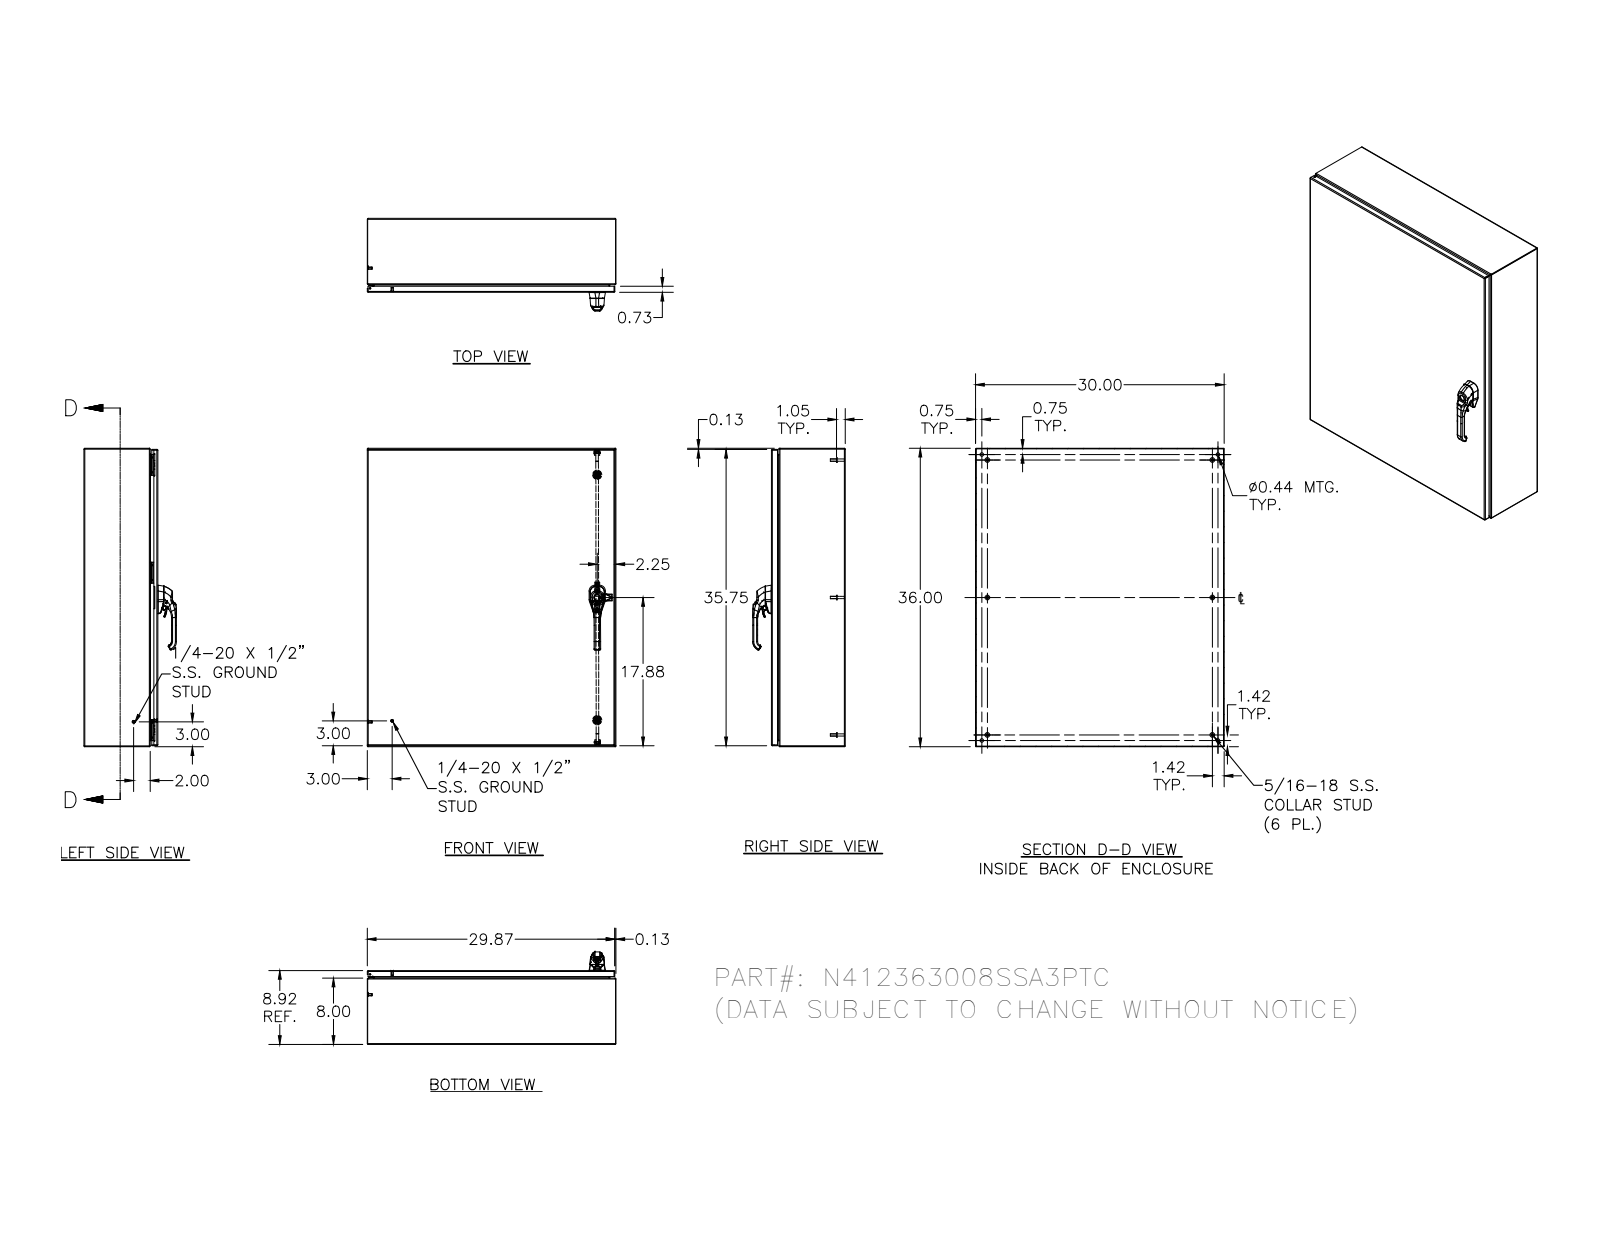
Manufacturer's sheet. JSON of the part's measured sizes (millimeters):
{"part_name": "N412363008SSA3PTC; N412363008SSA3PTCBKP; N4123630SSA3PTCLID; HFW328176 (+8 more)", "step_written_by": "Autodesk Inventor 2011 (AUTOMOTIVE_DESIGN)", "units": "millimeters", "bodies": {"solids": 74, "faces": 3524, "planar": 1171, "cylindrical": 1297, "other": 1056}, "overall_size": [914.4, 762, 283.6], "volume_mm3": 4411000, "surface_area_mm2": 4612000, "round_holes": [[4.8, 7], [2.4, 6], [3.9, 6], [4.2, 6], [4.2, 6], [4.4, 6], [5, 4], [11.1, 4], [4, 3], [5.4, 3], [2.7, 2], [4.1, 2]], "round_bosses_or_shafts": [[6.4, 14], [15, 6], [14.3, 6], [9.1, 6], [8.1, 6], [7.6, 6], [7, 6], [6.5, 6]], "partial_cylinders_radius": [[0.5, 186], [0.3, 100], [1.3, 38], [0.8, 34], [0.4, 26], [0.5, 23], [3, 23], [3.2, 21]], "face_to_face_distances": [1.9, 224.6, 222.7, 226.5, 760.1, 912.5, 758.2, 762, 914.4, 910.6], "hole_center_spacings": [330.2, 812.7, 482.5, 0.4, 16.8, 812.8, 0.5, 12.7]}
